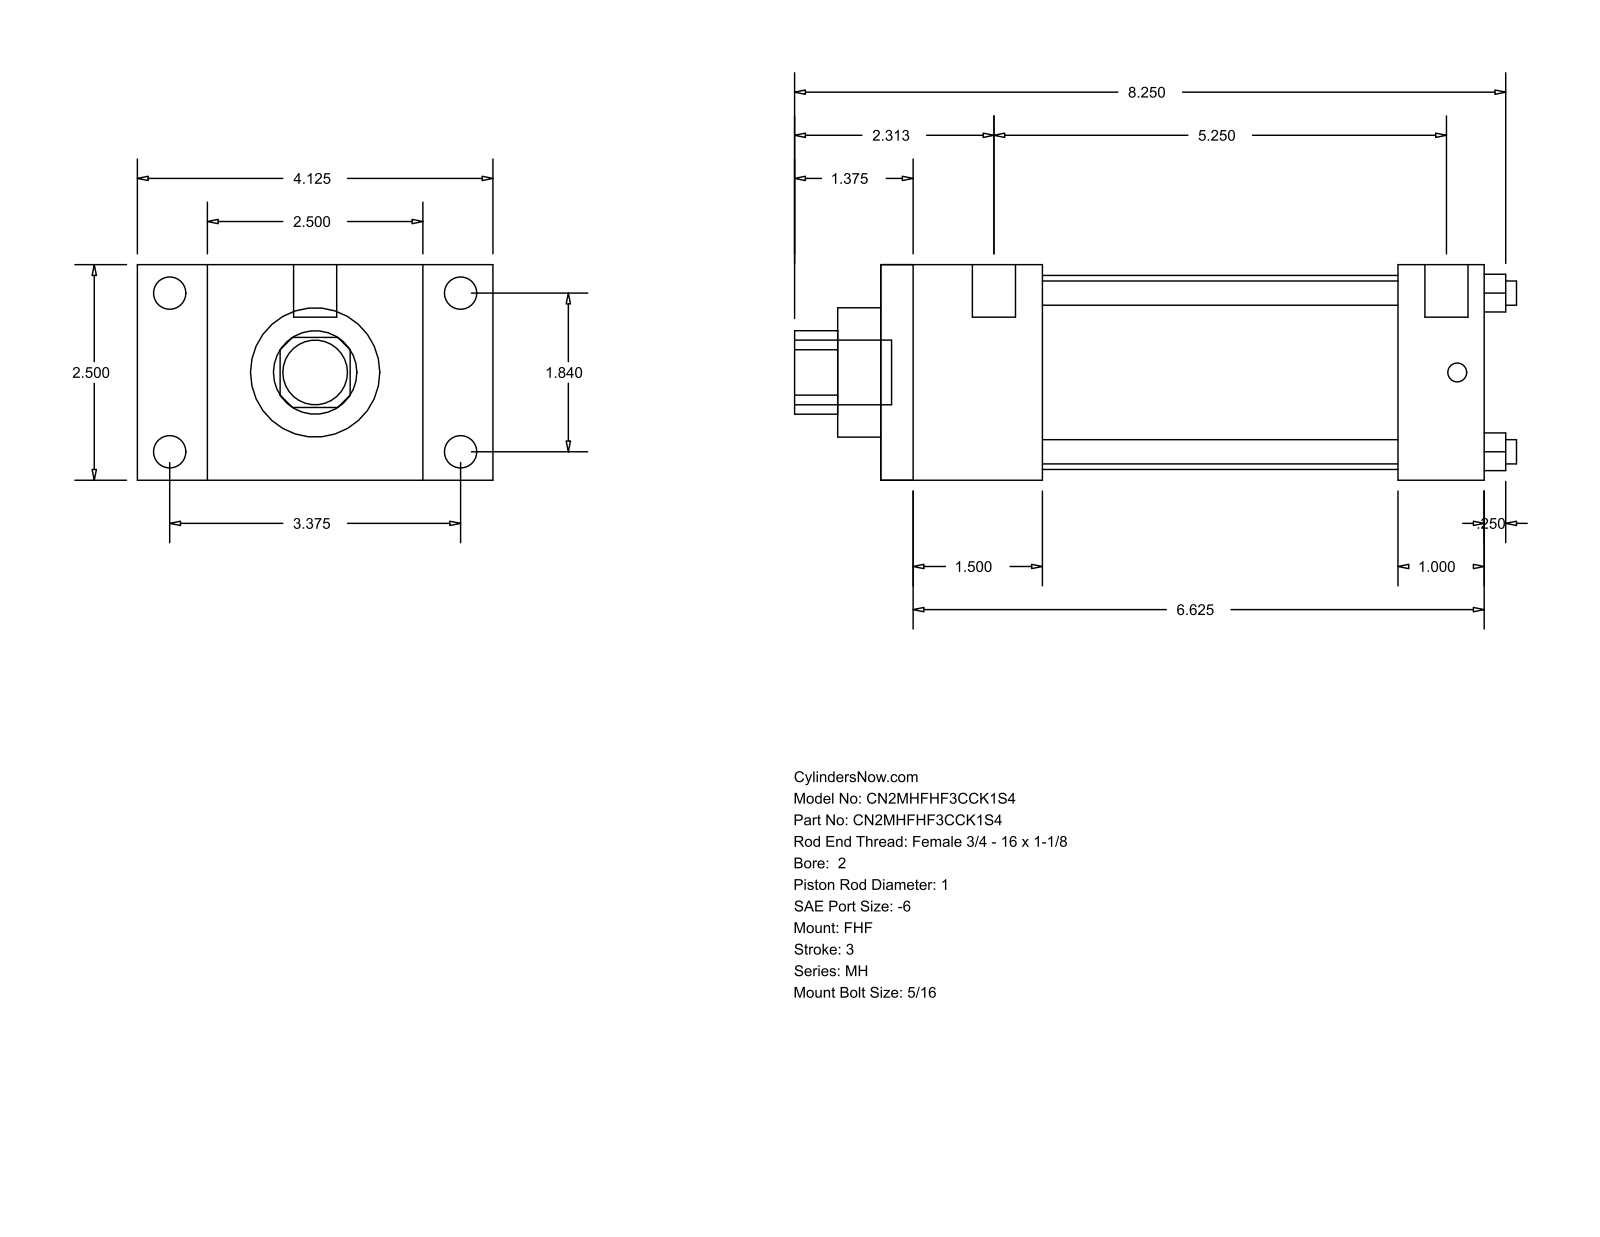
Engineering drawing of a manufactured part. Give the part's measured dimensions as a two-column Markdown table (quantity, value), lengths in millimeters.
| quantity | value |
| --- | --- |
| part name | MH_FHF__0200_1 |
| STEP written by | GSSL Pune (CONFIG_CONTROL_DESIGN) |
| units | millimeters |
| bodies | 0 solids, 88 faces (60 planar, 28 cylindrical, 0 other) |
| overall size | 212.72 × 104.78 × 63.5 |
| round holes (diameter × count) | 7.14 × 4, 25.4 × 1, 38.1 × 1, 57.15 × 1 |
| round bosses / shafts (diameter × count) | 9.53 × 4, 5.56 × 4, 12.7 × 2, 19.05 × 1 |
| partial cylindrical surfaces (radius × count) | 12.29 × 1 |
| main face-to-face distances | 63.5, 177.8, 47.63, 130.17, 20.64, 84.14, 104.78, 25.4, 104.77, 152.4 |
| hole center spacings | 33.05, 46.74, 66.1 |
